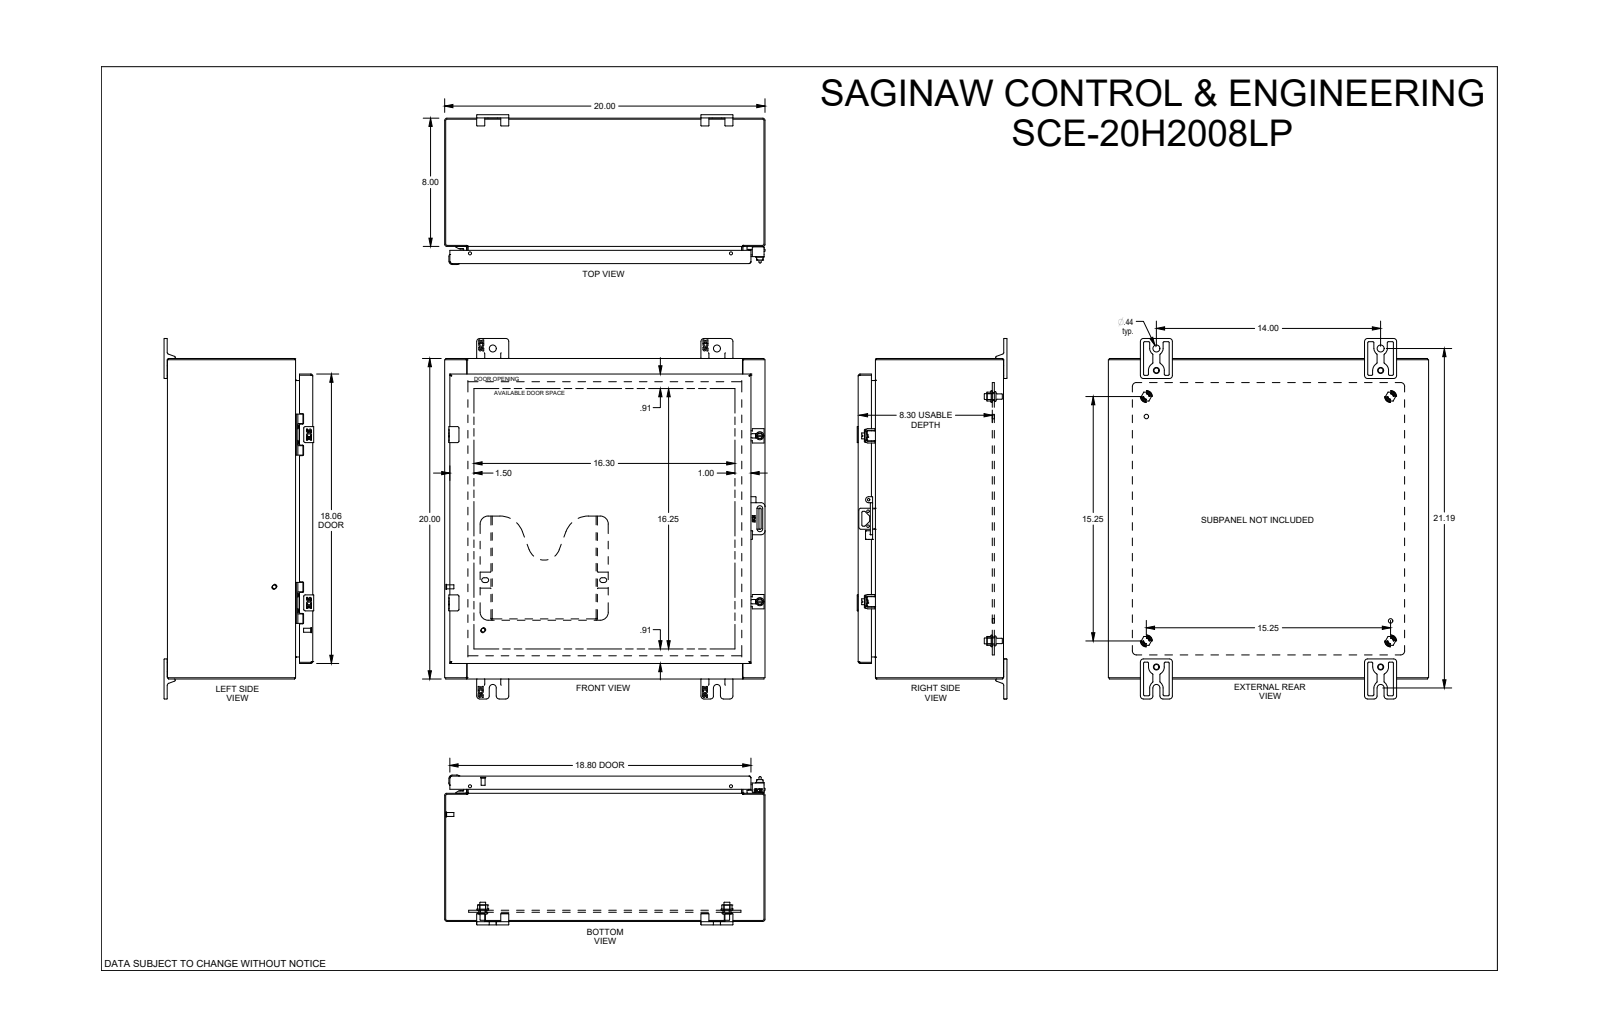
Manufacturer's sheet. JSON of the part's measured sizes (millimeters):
{"part_name": "SCE-20H2008LP", "step_written_by": "SolidWorks 2019 (CONFIG_CONTROL_DESIGN)", "units": "millimeters", "bodies": {"solids": 0, "faces": 4445, "planar": 1673, "cylindrical": 1177, "other": 1595}, "overall_size": [571.5, 508, 237.4], "round_holes": [[6.4, 5], [4.4, 4], [5.2, 4], [5.5, 4], [6.2, 4], [6.8, 4], [7.9, 4], [7.9, 4], [9.3, 4], [9.5, 4], [11.1, 4], [12.7, 4]], "round_bosses_or_shafts": [[6.3, 7], [4.3, 7], [6.4, 6], [14.3, 5], [15, 4], [9.6, 4], [9.3, 4], [8.4, 4]], "partial_cylinders_radius": [[0.6, 126], [0.3, 114], [0.4, 56], [1.6, 55], [0.8, 37], [0.7, 30], [1.5, 30], [4.7, 21]], "face_to_face_distances": [1.9, 506.1, 228.5, 226.6, 1.9, 230.5, 228.5, 504.2, 508, 12.7], "hole_center_spacings": [266.7, 0.5, 12.5, 25, 44.2, 373.8, 387.4, 428.9]}
